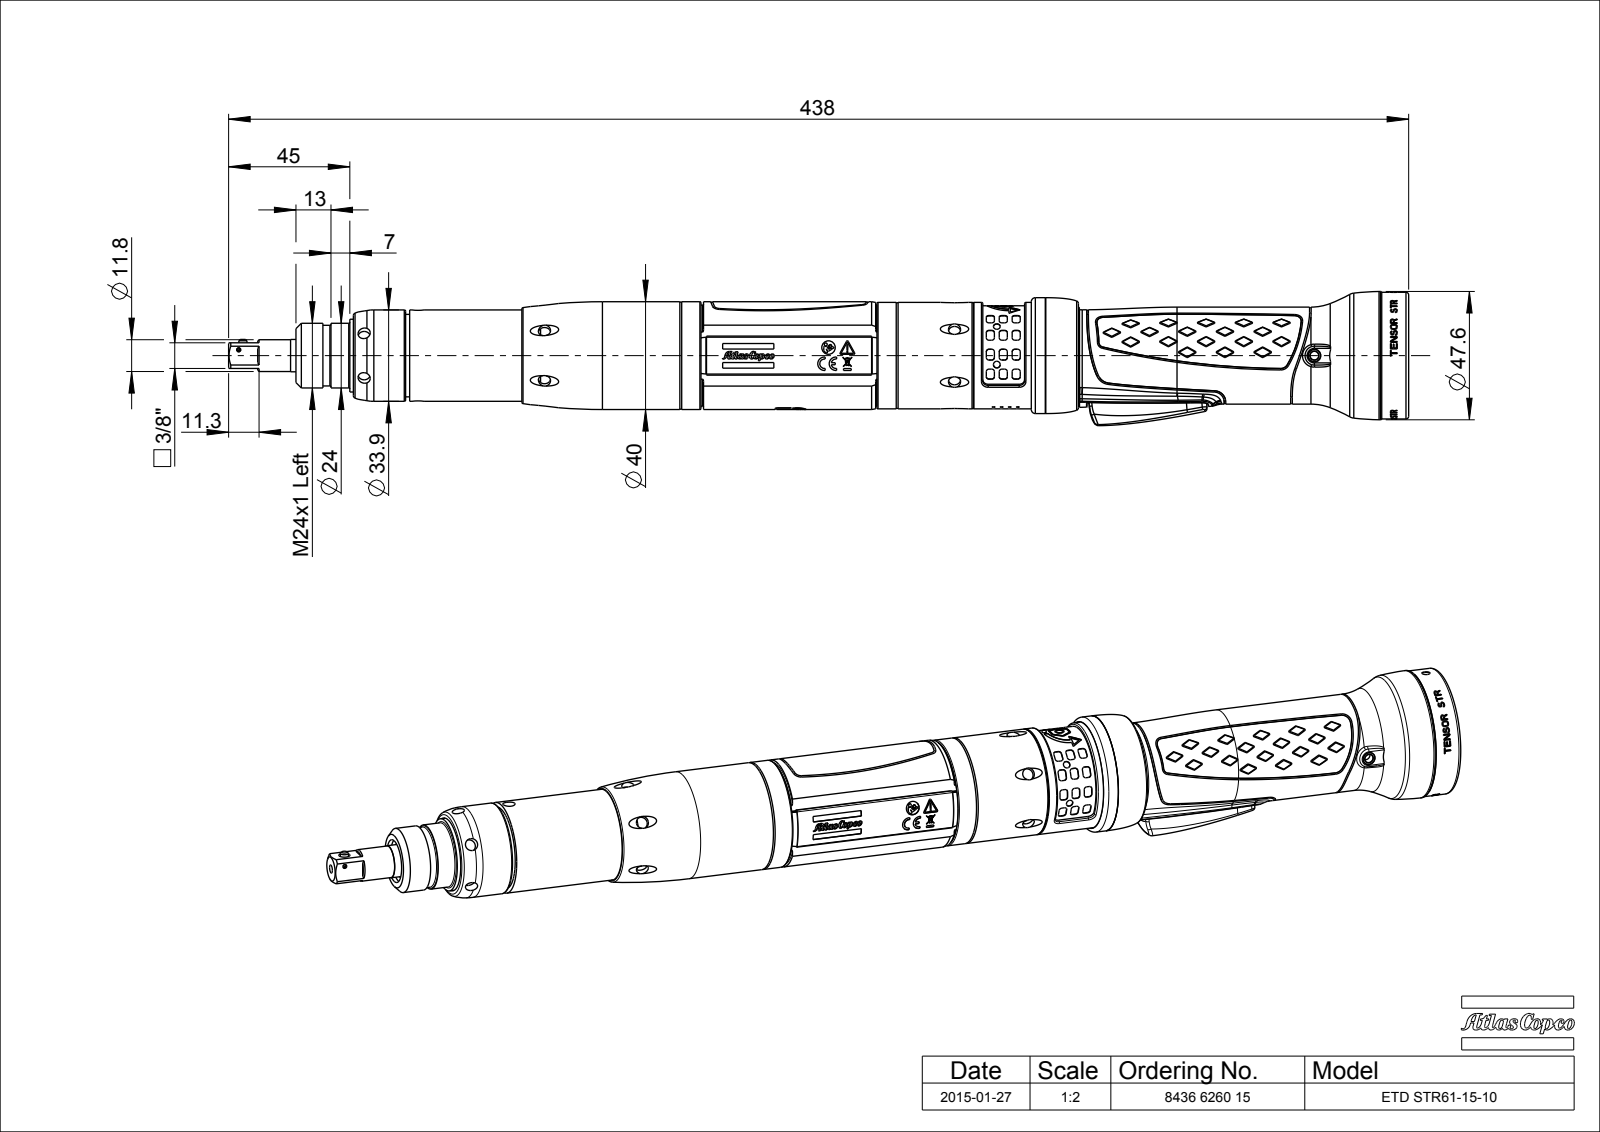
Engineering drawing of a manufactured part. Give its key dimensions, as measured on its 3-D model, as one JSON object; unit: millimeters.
{"part_name": "E2_SW0001; E1_SW0002; ASM0091_ASM", "step_written_by": "CREO PARAMETRIC BY PTC INC, 2022414 (CONFIG_CONTROL_DESIGN)", "units": "millimeters", "bodies": {"solids": 3, "faces": 4811, "planar": 1880, "cylindrical": 637, "other": 2294}, "overall_size": [438.6, 49.8, 47.6], "volume_mm3": 445700, "surface_area_mm2": 82060, "round_holes": [[1, 12], [4.5, 10], [1.6, 2], [0.4, 1], [0.7, 1], [1.2, 1], [1.5, 1], [3, 1], [3.2, 1], [3.9, 1], [4.7, 1], [5, 1]], "round_bosses_or_shafts": [[47, 1], [43, 1], [40, 1], [39.5, 1], [37.5, 1], [37, 1], [37, 1], [36.2, 1]], "partial_cylinders_radius": [[0.2, 58], [0.3, 44], [0.5, 43], [2, 14], [3, 12], [1.5, 5], [0.4, 4], [0.6, 4]], "face_to_face_distances": [0.5, 197.9, 3.6, 194.3, 162.1, 32.2, 35.8, 33.8, 37.7, 37.7], "hole_center_spacings": [3, 6, 9, 67.5, 151.7, 219.2, 5, 5.1]}
